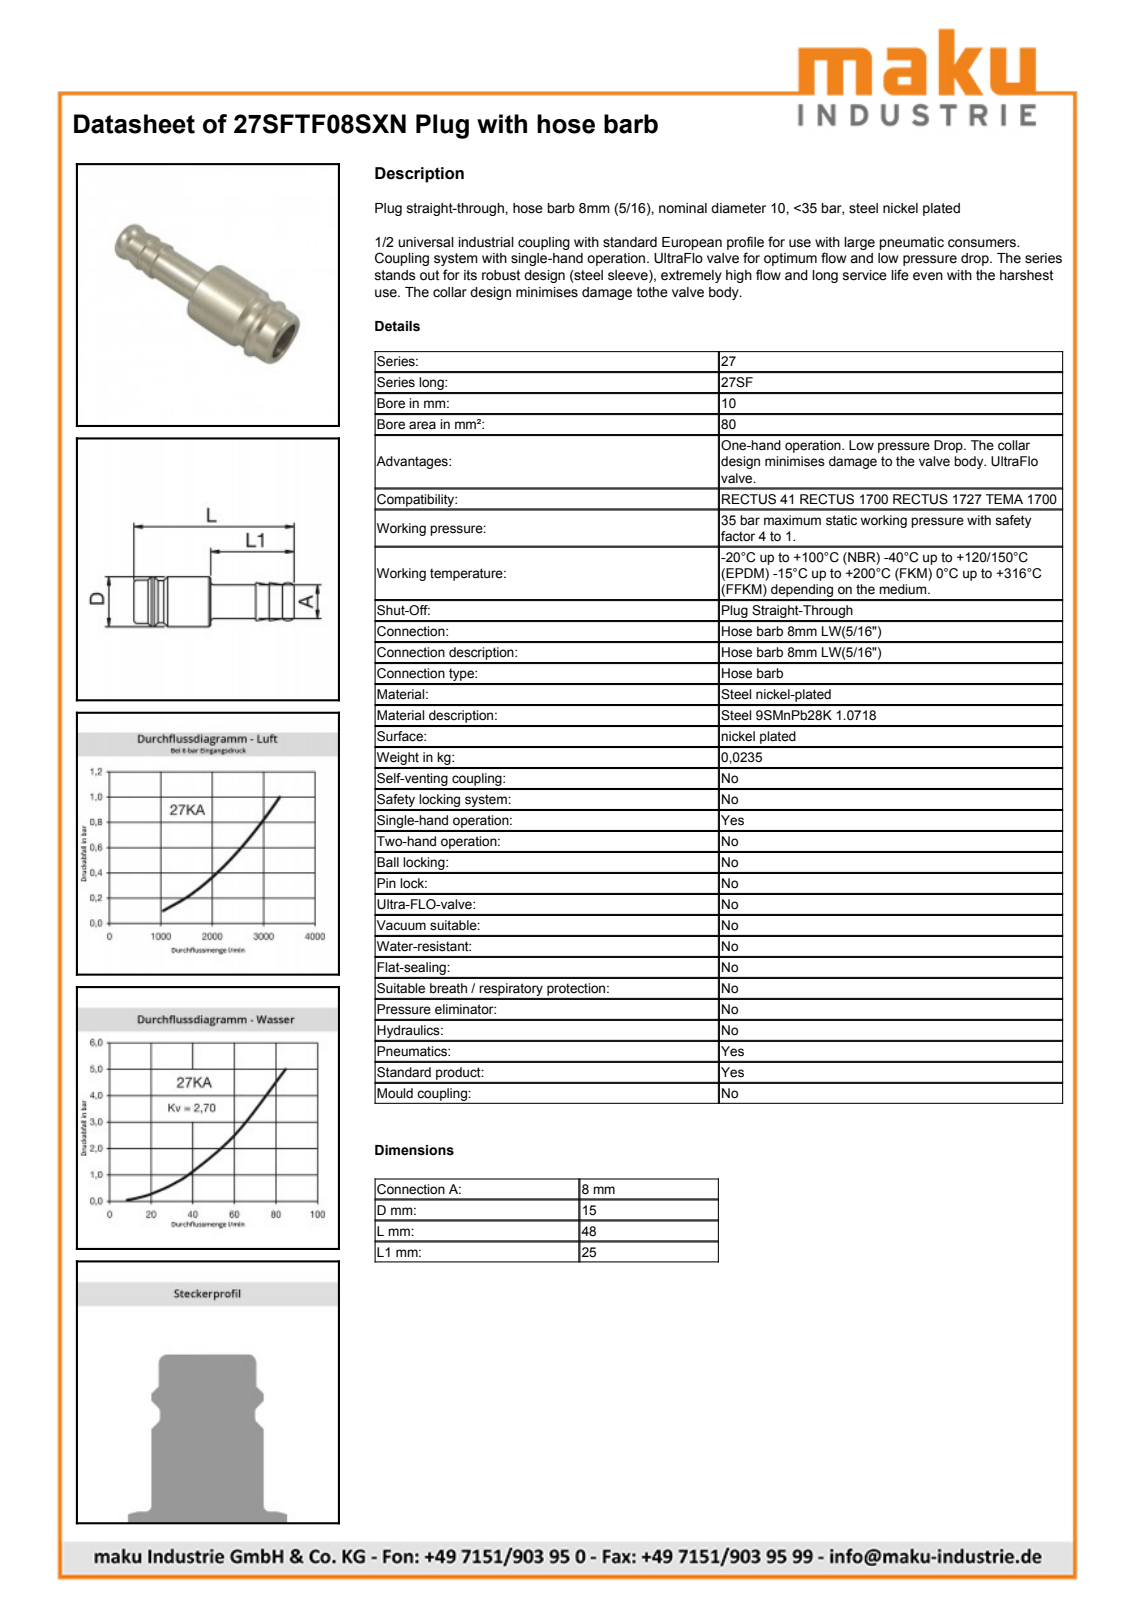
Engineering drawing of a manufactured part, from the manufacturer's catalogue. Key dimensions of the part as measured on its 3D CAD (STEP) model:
Part name (STEP PRODUCT): D103757
STEP written by: Autodesk Inventor 2011 (AUTOMOTIVE_DESIGN)
Units: millimetres
Bodies: 1 solid, 26 faces (4 planar, 7 cylindrical, 15 other)
Overall size (bounding box): 48 × 15 × 15
Volume: 3 020 mm³ · Surface area: 3 081 mm²
Round holes (diameter × count): ⌀6 ×1, ⌀9 ×1
Round bosses / shafts (diameter × count): ⌀15 ×1, ⌀13 ×1, ⌀12.65 ×1, ⌀8.1 ×1
Main face-to-face distances: 23, 48, 25, 36.5, 13.5, 11.5
